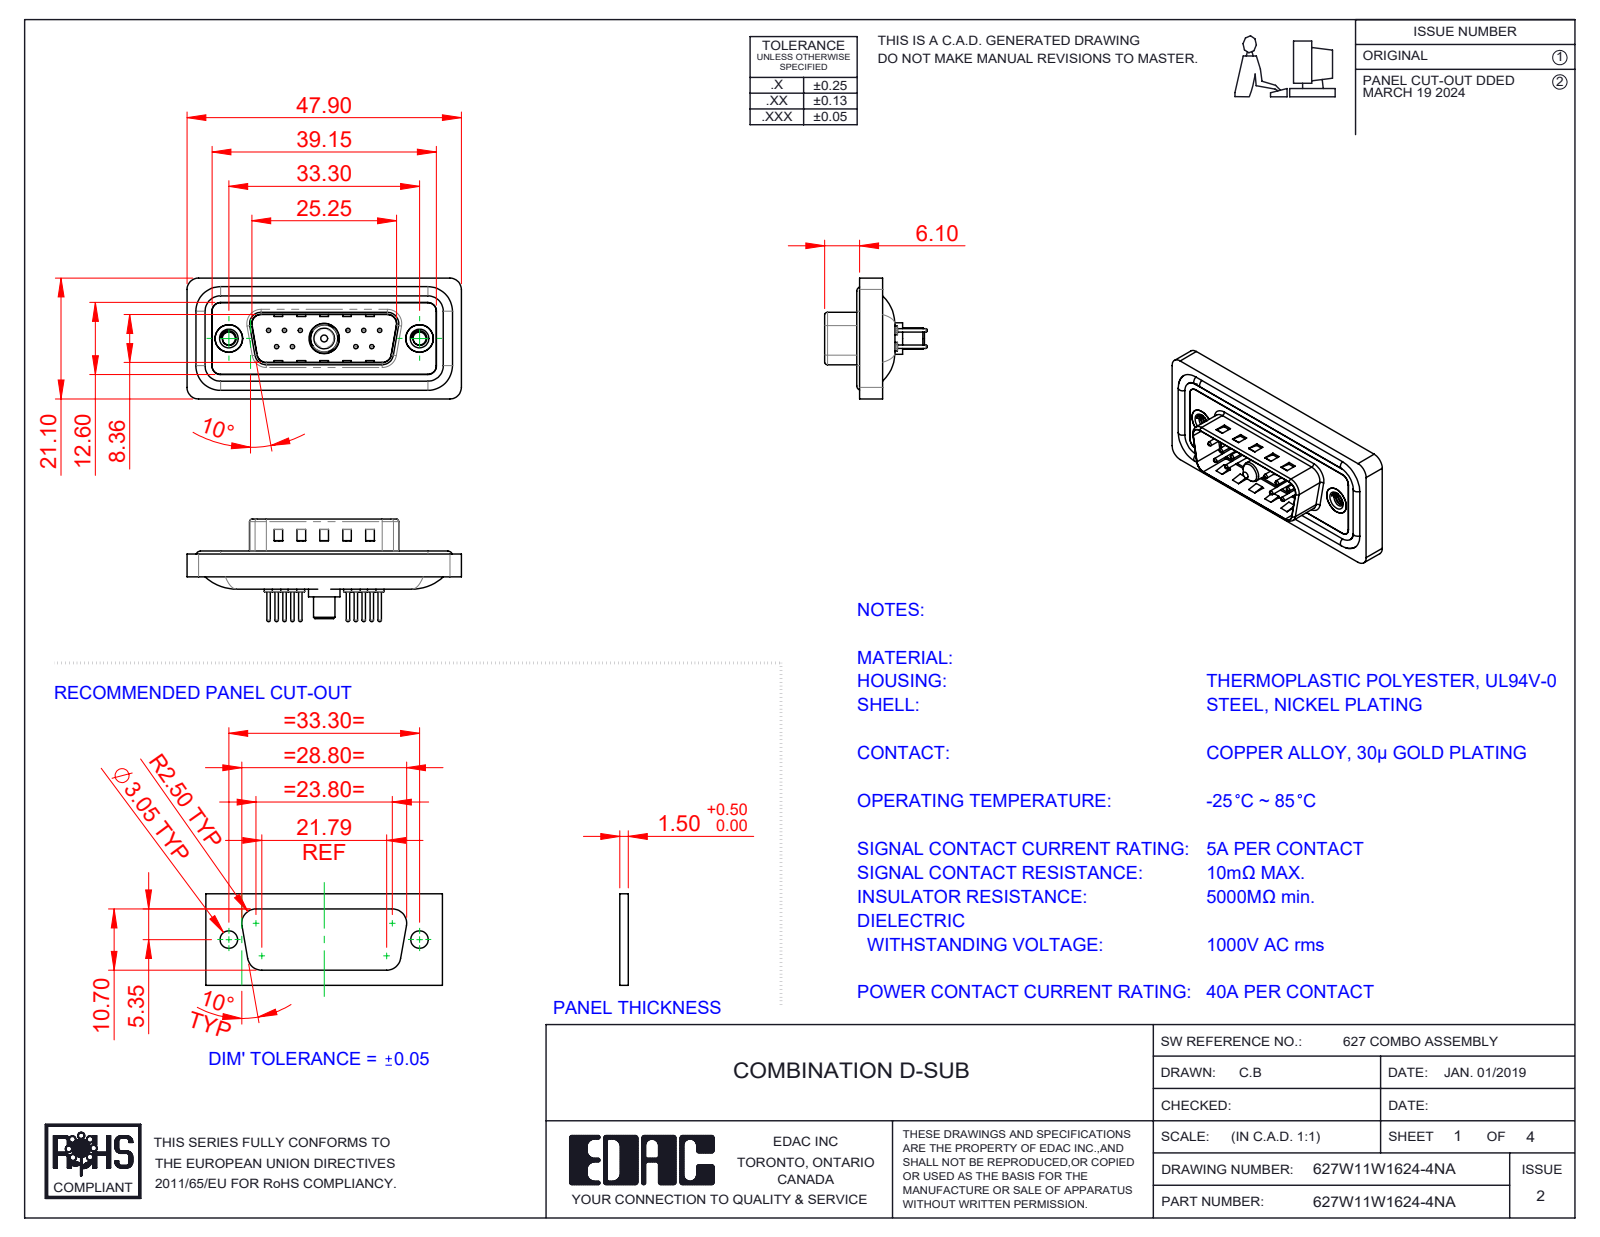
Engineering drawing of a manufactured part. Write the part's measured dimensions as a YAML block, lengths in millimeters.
part_name: "627Combo Housing_11W1; 627Combo Contact Row 1_24; 627Combo Threaded Rivet_A; 627W11W1624-4NA (+5 more)"
step_written_by: "SolidWorks 2023 (CONFIG_CONTROL_DESIGN)"
units: millimeters
bodies: {solids: 19, faces: 867, planar: 266, cylindrical: 349, other: 252}
overall_size: [47.9, 21.1, 17.9]
volume: 5468
surface_area: 8845
round_holes:
  - {diameter: 0.75, count: 10}
  - {diameter: 1.6, count: 10}
  - {diameter: 2, count: 10}
  - {diameter: 2.26, count: 2}
  - {diameter: 4, count: 2}
  - {diameter: 4.8, count: 2}
  - {diameter: 5, count: 2}
  - {diameter: 4.85, count: 1}
  - {diameter: 5.3, count: 1}
round_bosses_or_shafts:
  - {diameter: 1.5, count: 10}
  - {diameter: 0.6, count: 10}
  - {diameter: 1.6, count: 4}
  - {diameter: 4.9, count: 2}
  - {diameter: 5.5, count: 1}
  - {diameter: 5.2, count: 1}
  - {diameter: 4.75, count: 1}
  - {diameter: 3.75, count: 1}
partial_cylinders:
  - {radius: 1.5, count: 26}
  - {radius: 2, count: 20}
  - {radius: 0.5, count: 8}
  - {radius: 1.6, count: 8}
  - {radius: 1, count: 7}
  - {radius: 0.25, count: 4}
  - {radius: 0.6, count: 4}
  - {radius: 0.65, count: 4}
face_to_face_distances: [0.4, 1.1, 1.6, 1.5, 0.5, 2.9, 3.1, 2.5, 4.1, 0.82]
hole_center_spacings: [3.16, 2.77, 13.85, 11.08, 16.62, 5.03, 5.04, 5.54]
